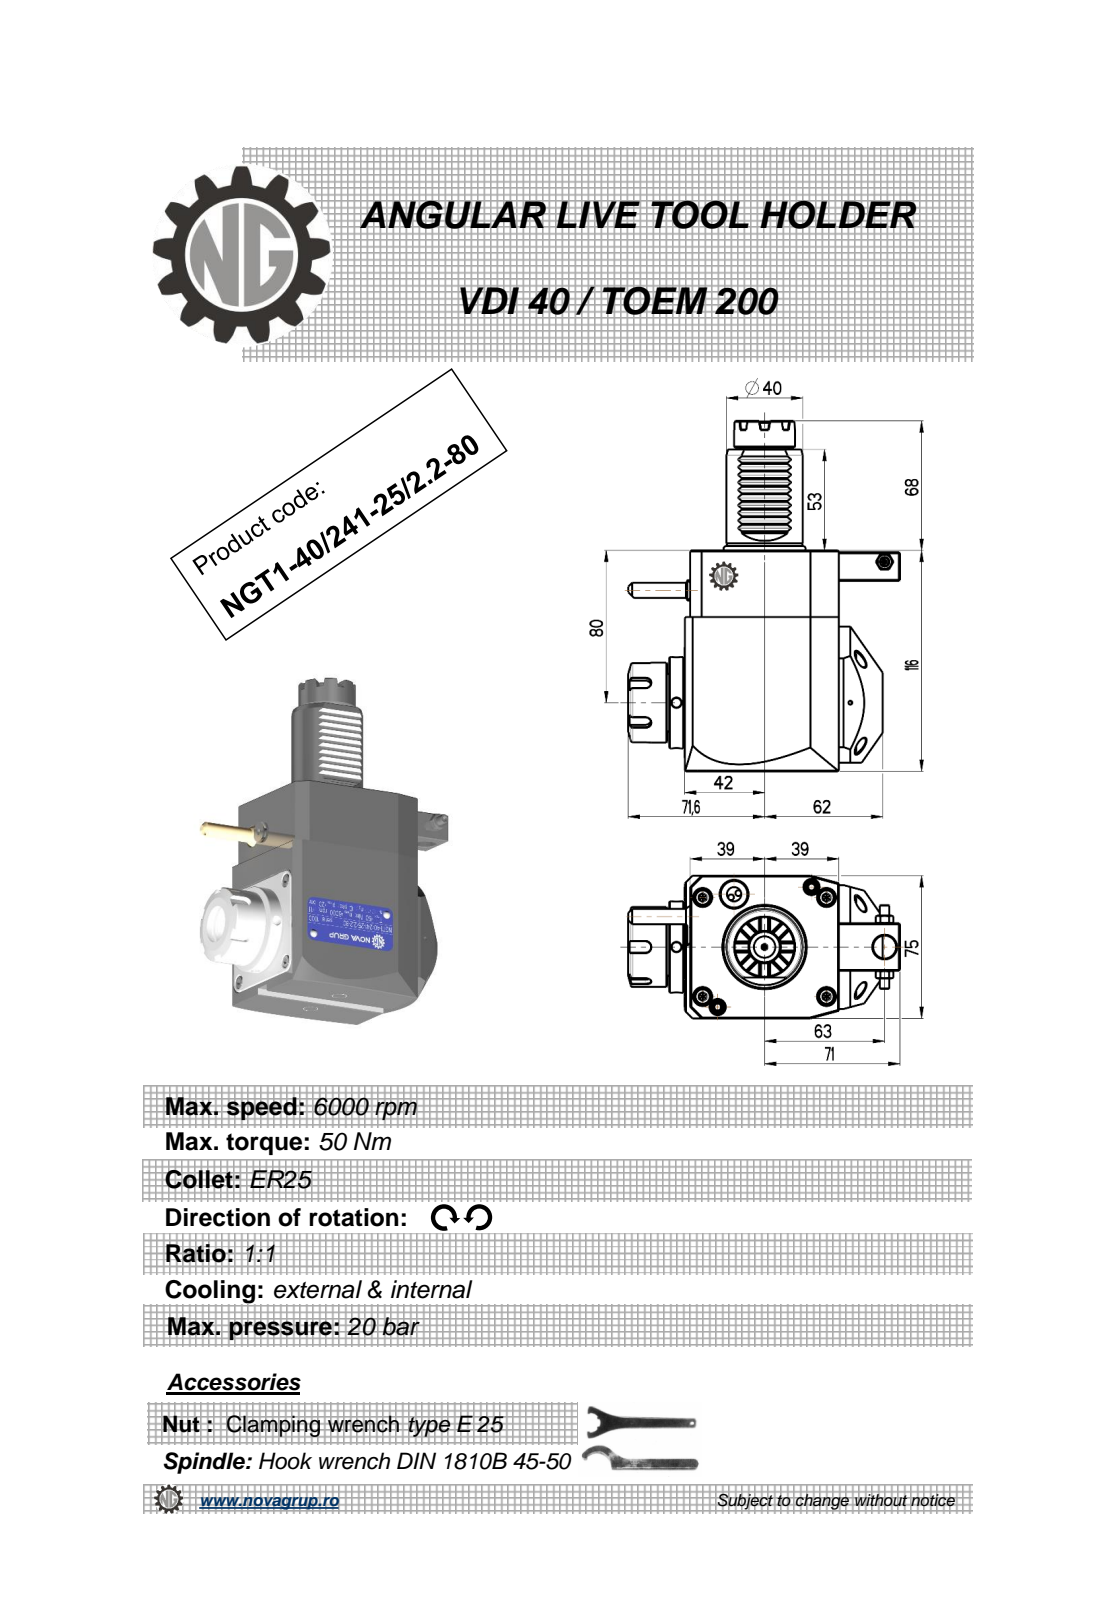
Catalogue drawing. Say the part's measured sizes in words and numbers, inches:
The part is named "NGT1_40_241_25_2_2_80". Its 3-D file was written by "PRO/ENGINEER BY PARAMETRIC TECHNOLOGY CORPORATION, 2010280 (CONFIG_CONTROL_DESIGN)". It is 1 solid with 508 faces: 222 planar, 97 cylindrical and 189 other. Overall it measures 7.244 by 5.614 by 3.016 inches. Its volume is 53.29 cubic inches and its surface area 110.7 square inches. Round holes: 3 of diameter 0.197, 1 of diameter 0.118, 1 of diameter 0.165, 1 of diameter 0.374, 1 of diameter 0.472, 1 of diameter 0.799. Round bosses or shafts: 1 of diameter 1.89, 1 of diameter 1.654, 1 of diameter 1.575, 1 of diameter 1.476, 1 of diameter 1.299, 1 of diameter 1.26, 1 of diameter 0.669, 1 of diameter 0.441. Partial cylindrical surfaces (rounded edges, fillets, slot ends): 12 of radius 0.01, 10 of radius 0.012, 6 of radius 0.009, 5 of radius 0.118, 1 of radius 0.02, 1 of radius 0.339, 1 of radius 1.575. The main face-to-face distances are 2.953, 4.567, 3.189, 3.071, 0.118, 0.11, 3.181, 4.409, 0.984, 0.295. The hole center spacings are 0.824, 2.407, 2.854, 4.301, 5.195.
